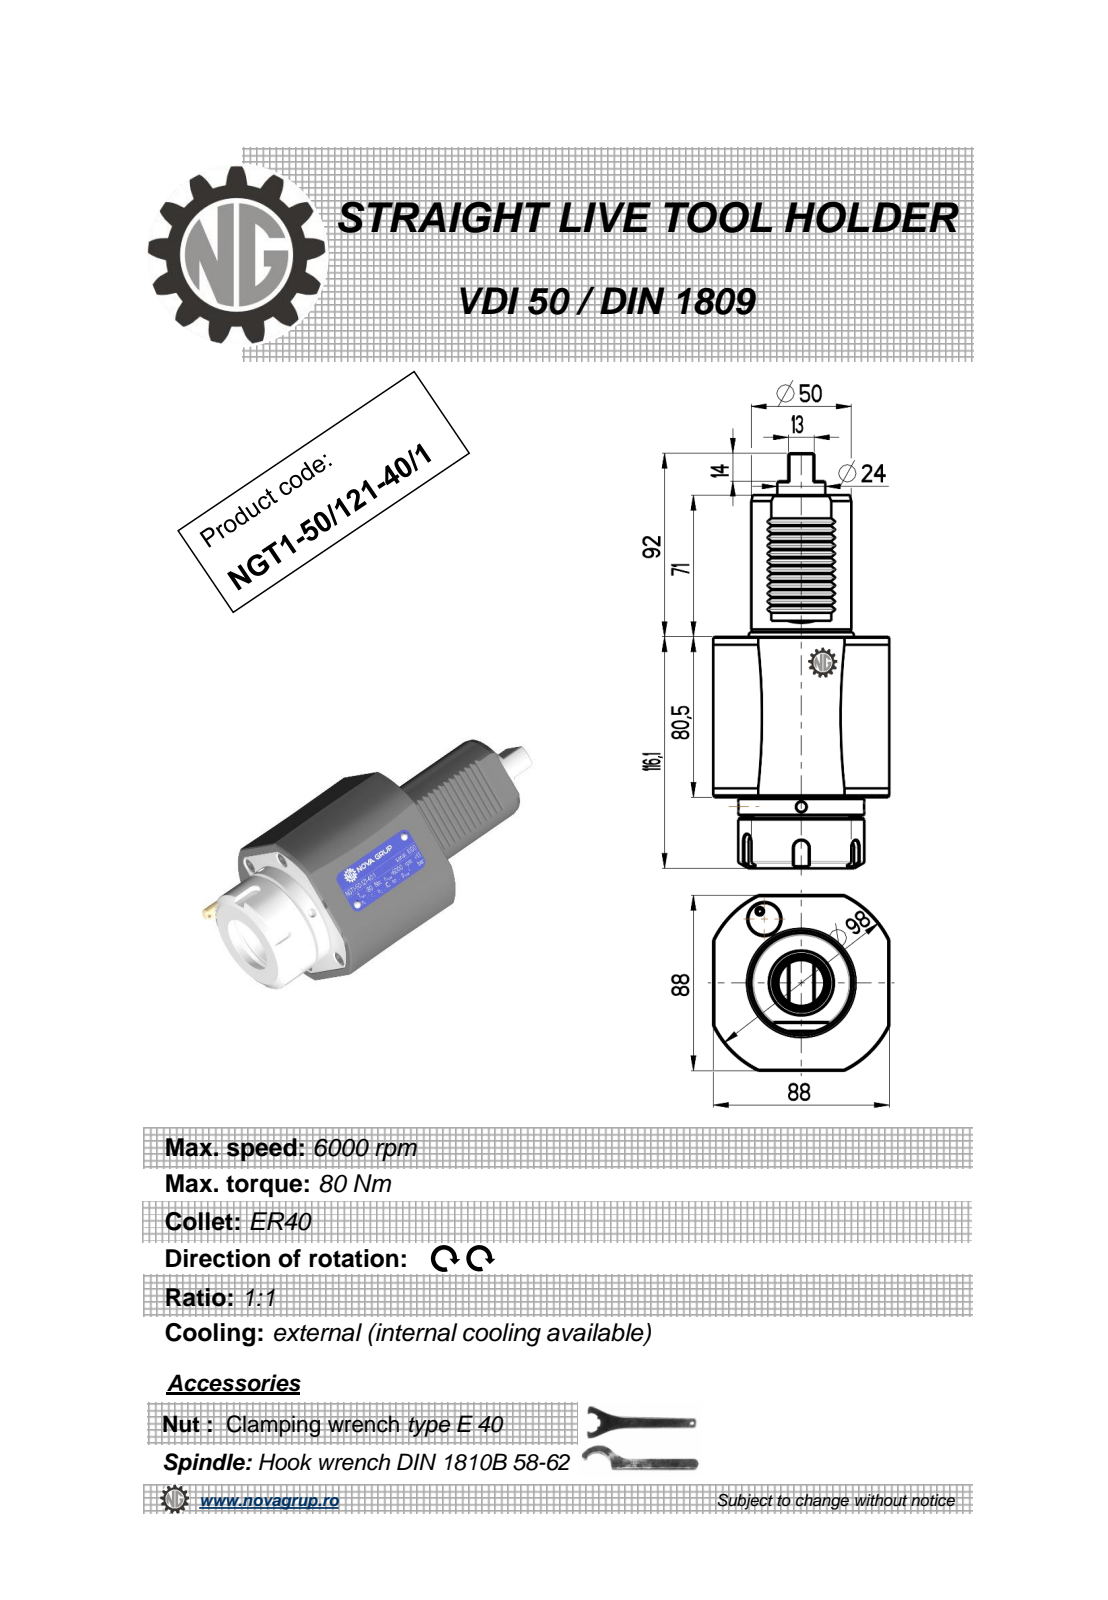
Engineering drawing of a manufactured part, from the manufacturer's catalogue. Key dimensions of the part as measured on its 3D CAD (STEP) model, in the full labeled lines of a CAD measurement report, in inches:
Part name (STEP PRODUCT): NGT1_50_121_40_1
STEP written by: PRO/ENGINEER BY PARAMETRIC TECHNOLOGY CORPORATION, 2010280 (CONFIG_CONTROL_DESIGN)
Units: inches
Bodies: 1 solid, 263 faces (110 planar, 63 cylindrical, 90 other)
Overall size (bounding box): 8.193 × 3.528 × 3.465
Volume: 48.47 in³ · Surface area: 100.4 in²
Round holes (diameter × count): ⌀0.197 ×2, ⌀0.098 ×1, ⌀0.118 ×1, ⌀1.319 ×1
Round bosses / shafts (diameter × count): ⌀2.48 ×1, ⌀2.008 ×1, ⌀1.969 ×1, ⌀0.945 ×1, ⌀0.354 ×1, ⌀0.276 ×1, ⌀0.197 ×1
Partial cylindrical surfaces — rounded edges, fillets, slot ends (radius × count): R0.012 ×12, R0.148 ×5, R0.031 ×2, R1.929 ×1
Main face-to-face distances: 3.465, 3.169, 4.571, 1.402, 4.327, 1.157, 0.244, 2.795, 5.965, 7.122
Hole centre spacings: 1.634
